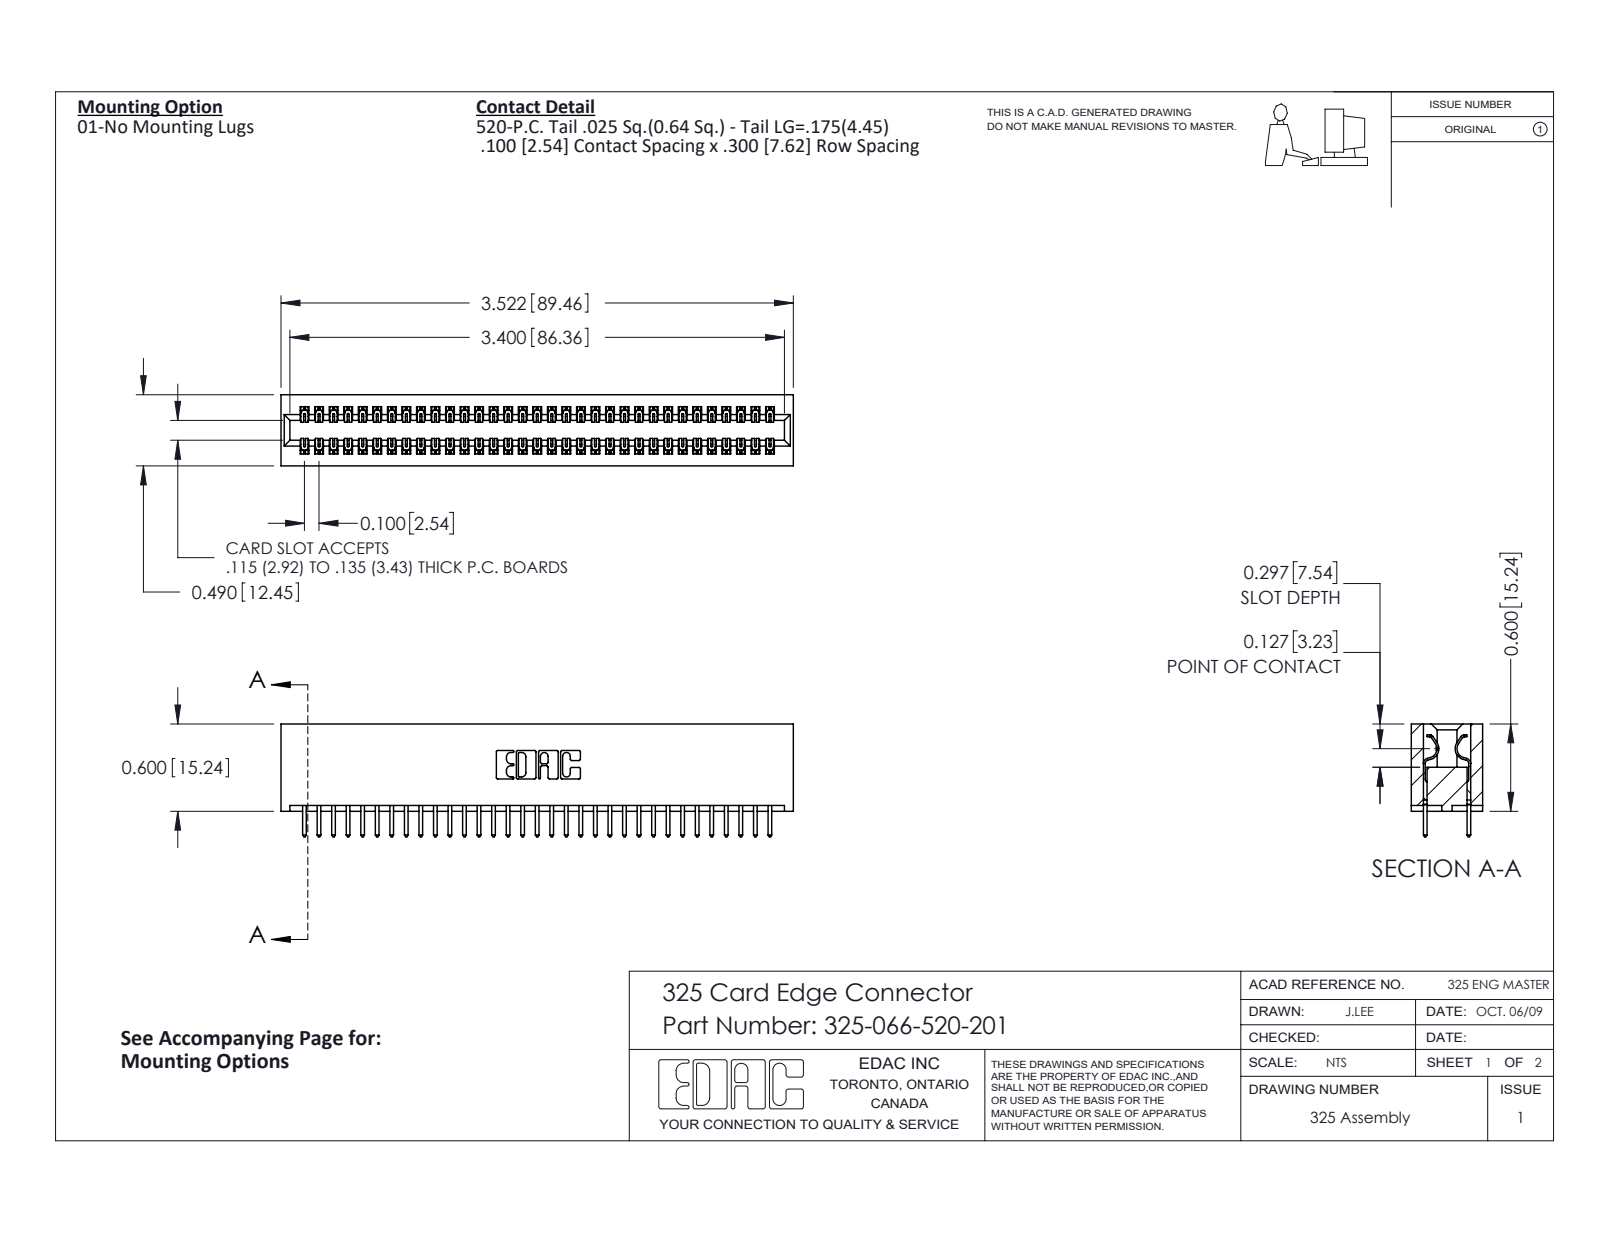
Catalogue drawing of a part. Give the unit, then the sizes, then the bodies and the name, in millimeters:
Units: millimetres
Overall size (bounding box): 89.5 × 19.7 × 12.4
Partial cylindrical surfaces — rounded edges, fillets, slot ends (radius × count): R0.2 ×99, R0.3 ×66, R0.3 ×22, R0.2 ×6, R0.8 ×6, R0.7 ×3, R0.4 ×2, R0.6 ×2
Main face-to-face distances: 2.1, 10.3, 7.6, 12.4, 2.7, 9.7, 0.6, 8.3, 7, 14.2
Volume: 12 100 mm³ · Surface area: 14 920 mm²
Bodies: 67 solids, 3538 faces (2442 planar, 1096 cylindrical, 0 other)
Part name (STEP PRODUCT): 325-292-001_325-293-120; 325 Part_Lugless; 325-066-520-201
STEP written by: SolidWorks 2016 (CONFIG_CONTROL_DESIGN)
